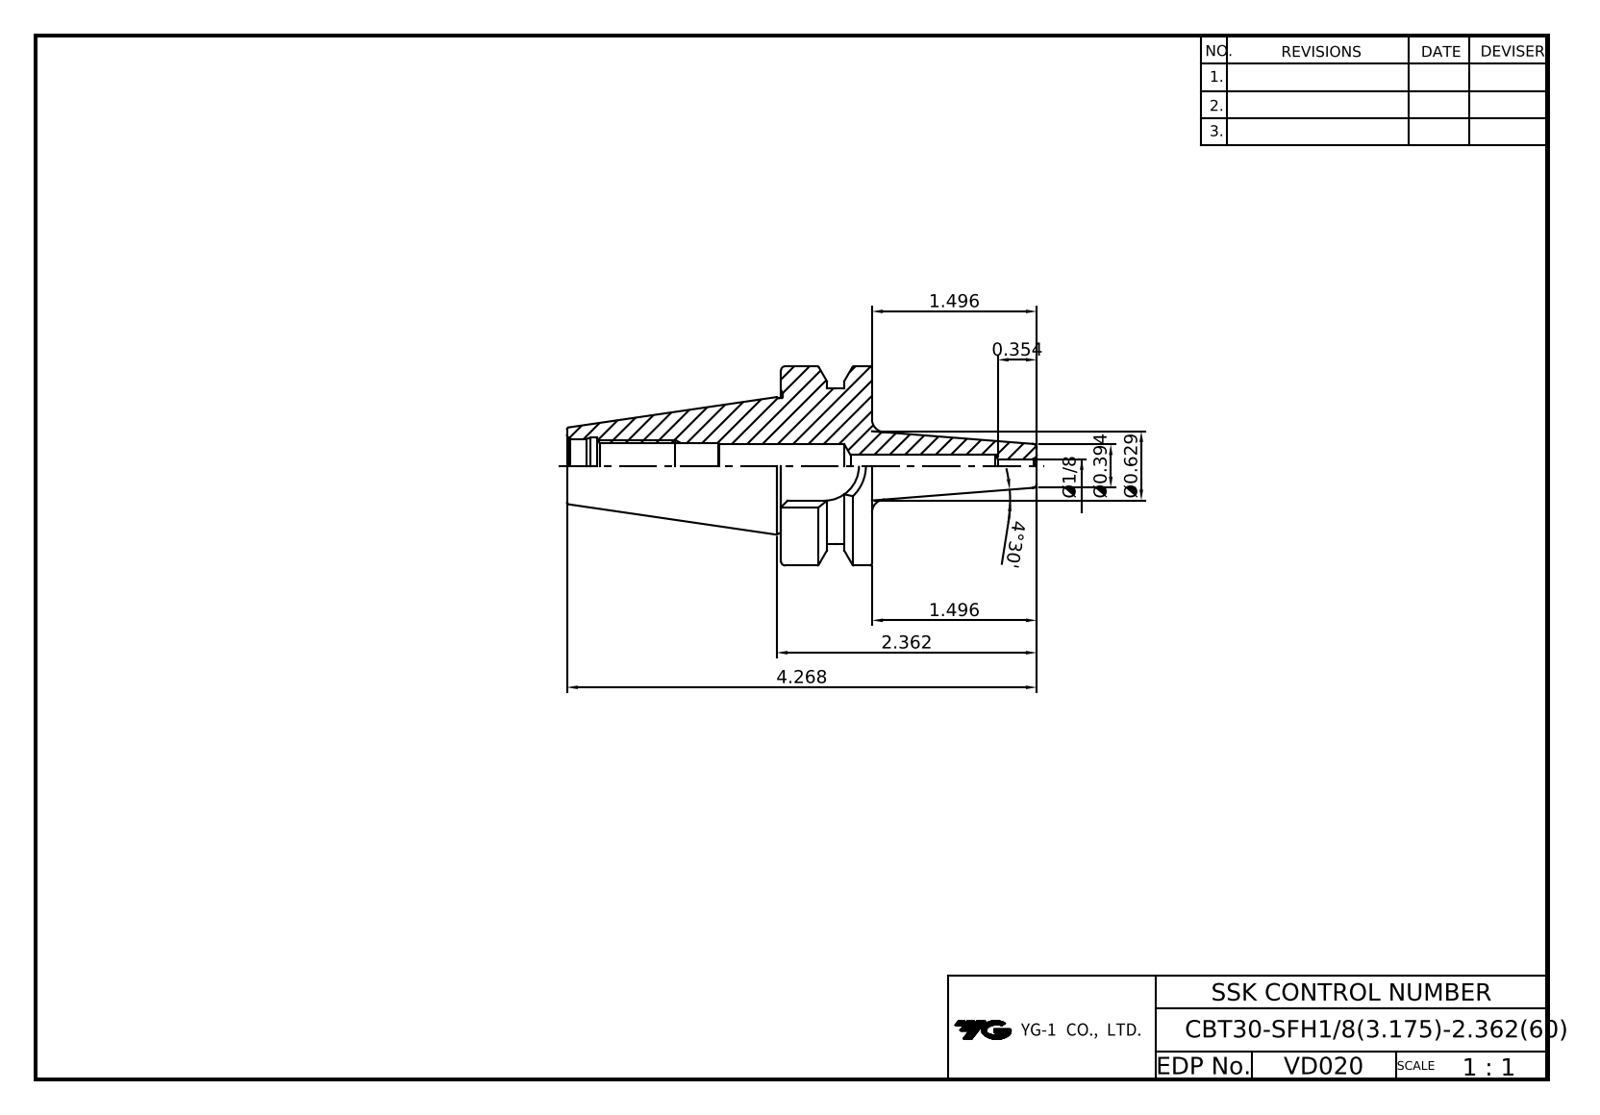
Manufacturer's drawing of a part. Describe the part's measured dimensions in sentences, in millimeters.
The part is named "CBT30SHANK_3D_20131112". Its 3-D file was written by "CREO PARAMETRIC BY PTC INC, 2018500 (CONFIG_CONTROL_DESIGN)". It is 1 solid with 100 faces: 26 planar, 28 cylindrical and 46 other. Overall it measures 108.4 by 46 by 46 millimeters. Its volume is 52 281 cubic millimeters and its surface area 15 102 square millimeters. Round holes: 1 of diameter 3.17, 1 of diameter 5, 1 of diameter 10, 1 of diameter 10.2, 1 of diameter 12, 1 of diameter 12.5, 1 of diameter 13.1. Round bosses or shafts: 1 of diameter 46, 1 of diameter 31.2. Partial cylindrical surfaces (rounded edges, fillets, slot ends): 1 of radius 8.05, 1 of radius 18. The main face-to-face distances are 21, 32.6, 14.63, 6.37, 10.63, 4, 10.37, 0.4, 10.23, 14.23.
